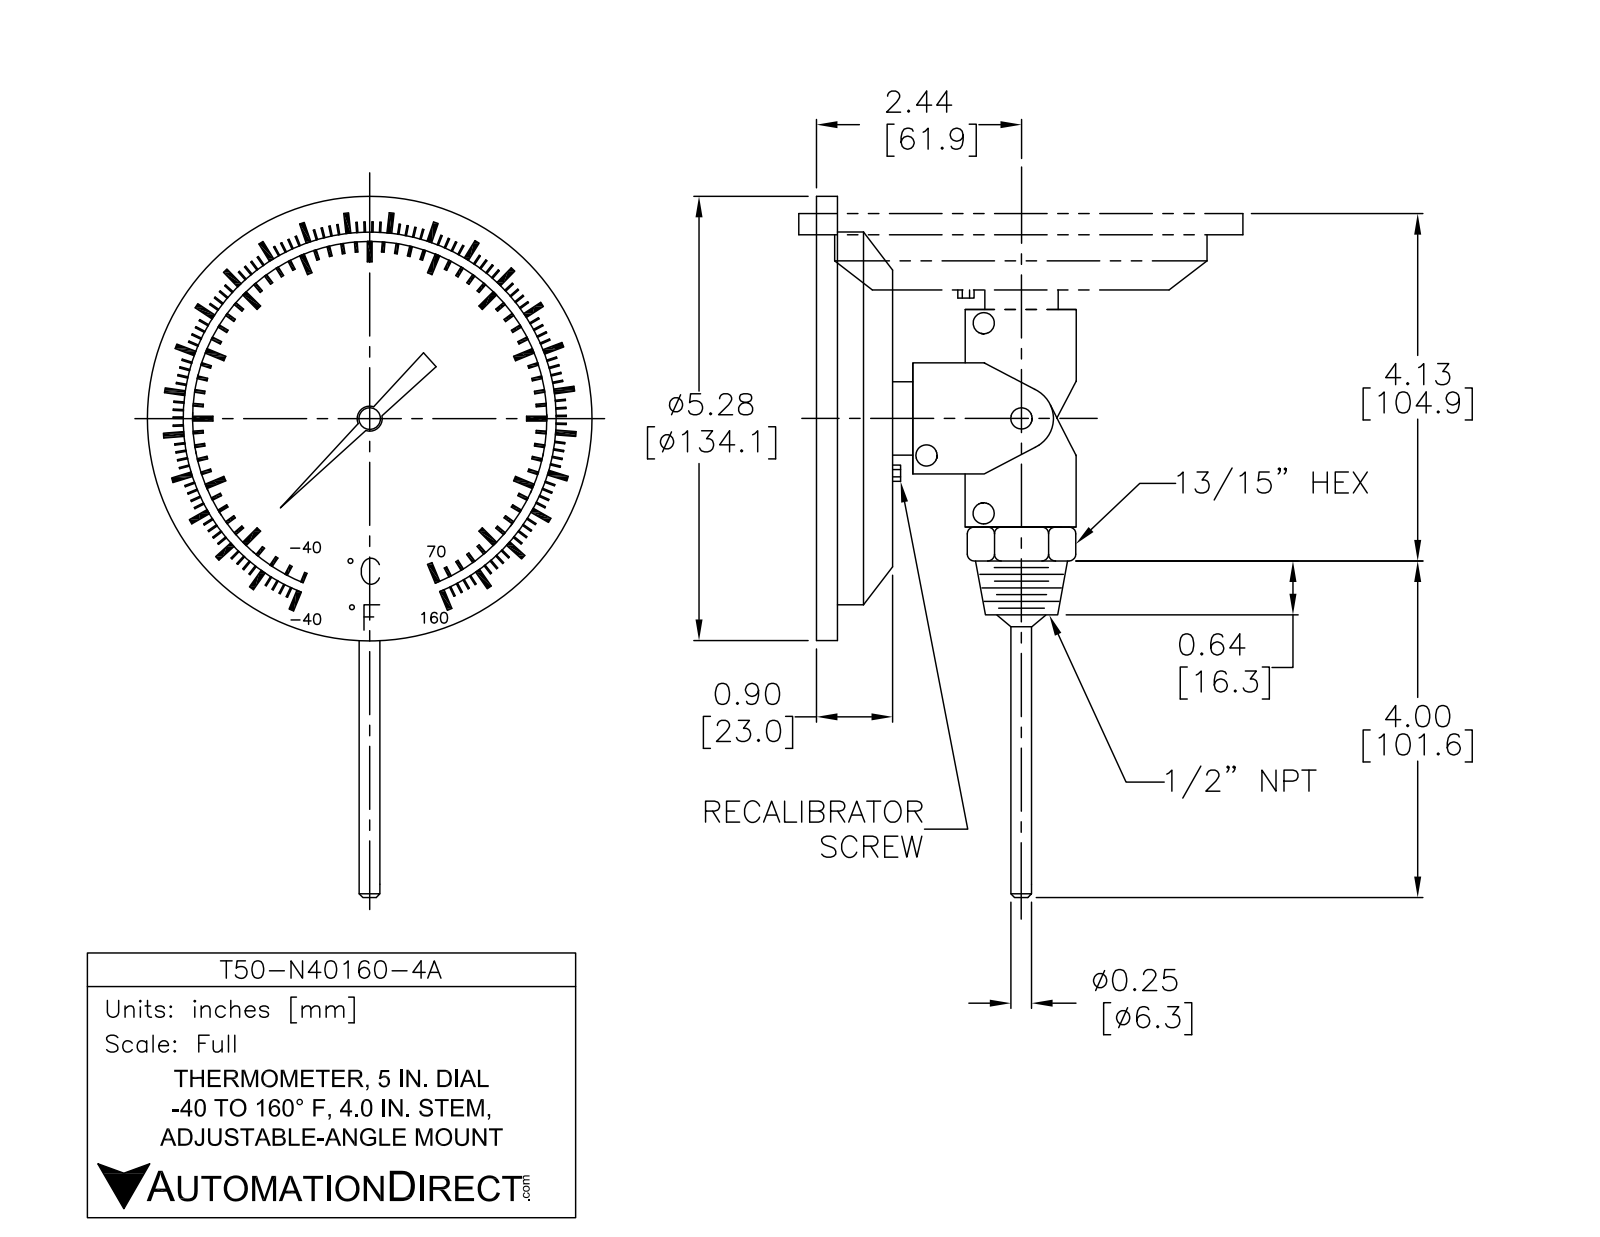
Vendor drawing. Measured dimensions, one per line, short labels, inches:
name: T50-N40160-4A
written by: SolidWorks 2021 (AUTOMOTIVE_DESIGN)
unit: in
bodies: 1 solid, 500 faces (320 planar, 45 cylindrical, 135 other)
size: 7.96 × 5.28 × 5.28
volume: 10.13 in³; area: 96.8 in²
holes: 1× ⌀3.424, 1× ⌀3.7, 1× ⌀4.76, 1× ⌀4.836
bosses: 4× ⌀0.305, 2× ⌀0.145, 1× ⌀5.28, 1× ⌀4.97, 1× ⌀3.73, 1× ⌀3.454, 1× ⌀0.85, 1× ⌀0.822
rounds: 10× R0.06, 4× R0.04, 1× R0.17, 1× R0.336, 1× R0.336, 1× R0.342, 1× R0.4
face distances: 0.353, 0.074, 0.055, 0.427, 1.19, 0.815, 0.462, 0.388, 1.245, 2.435
